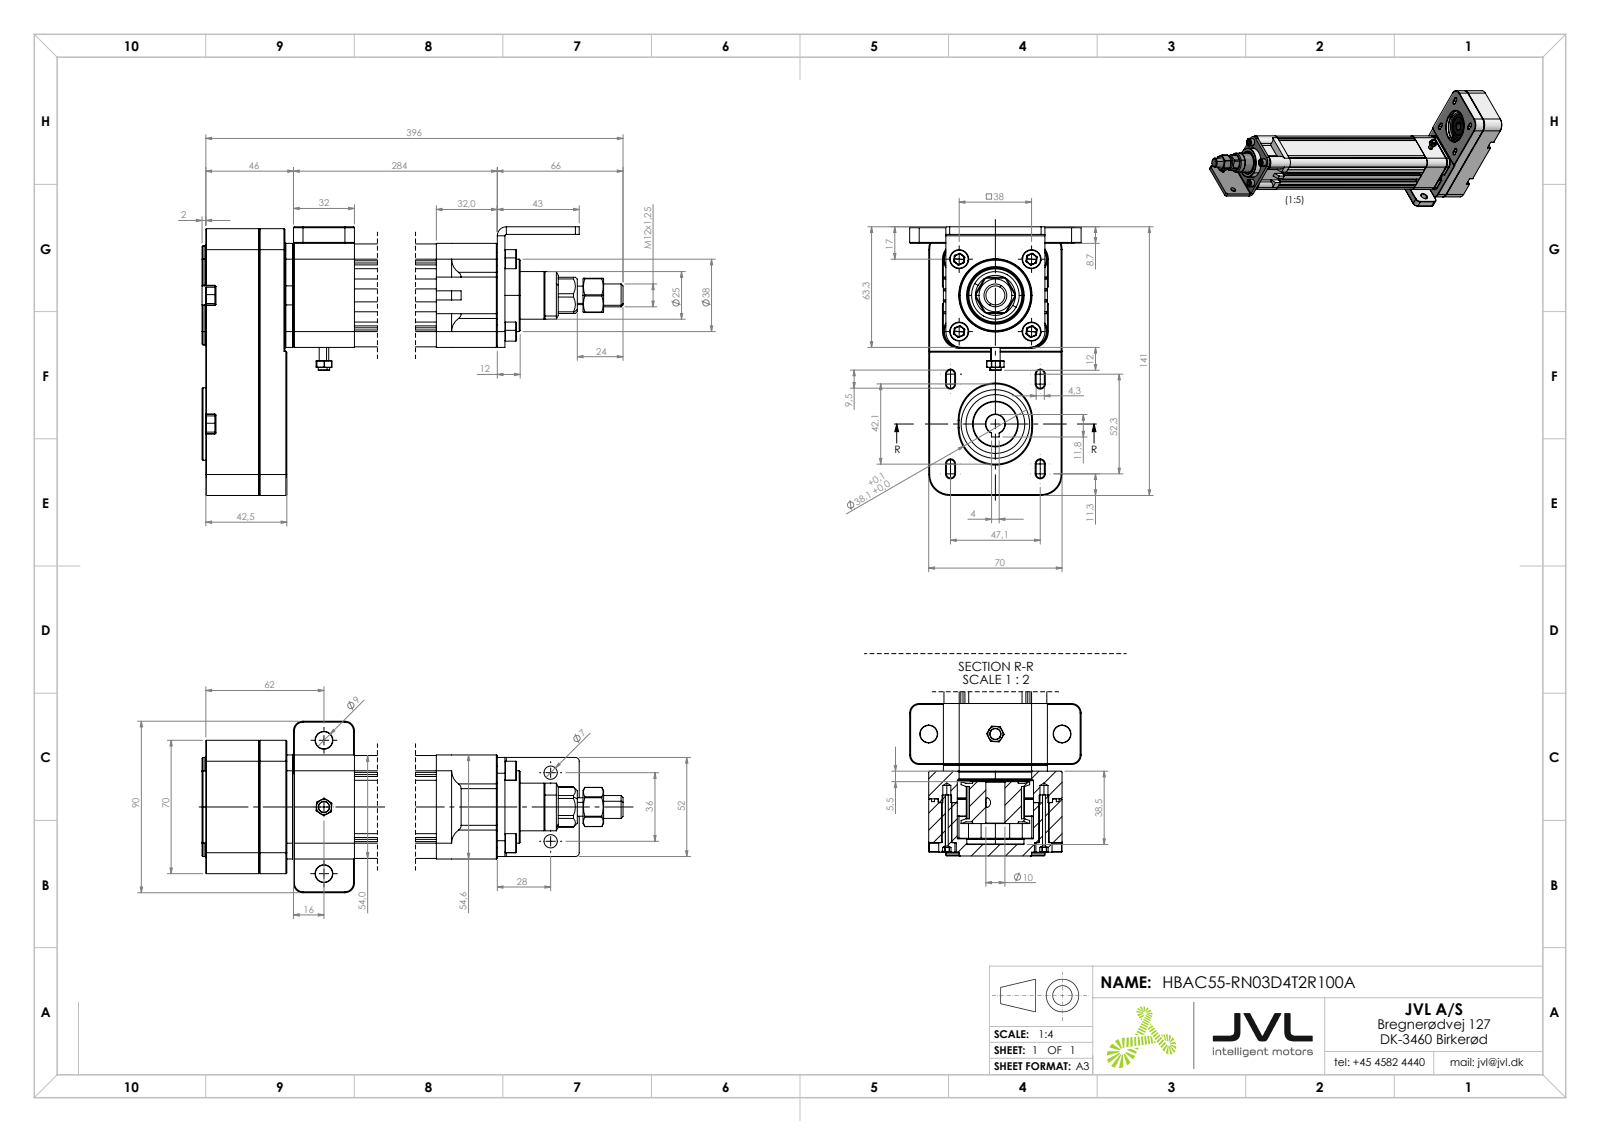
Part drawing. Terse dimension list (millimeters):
name: HBAC55 (CONFIGURABLE); HBAC55-NUT M12x1,25; HBAC55-Back piece T2; HBAC55-M5x25 (+8 more)
written by: SolidWorks 2023 (AUTOMOTIVE_DESIGN)
unit: mm
bodies: 24 solids, 2089 faces (695 planar, 810 cylindrical, 584 other)
size: 398 × 141 × 90
volume: 710 310 mm³; area: 291 163 mm²
holes: 8× ⌀4.2, 6× ⌀5, 5× ⌀1.5, 5× ⌀5.3, 4× ⌀6.4, 4× ⌀6.5, 4× ⌀9.5, 4× ⌀10, 2× ⌀5.5, 2× ⌀7, 2× ⌀9, 2× ⌀11
bosses: 8× ⌀5, 7× ⌀8.5, 6× ⌀10, 5× ⌀6, 2× ⌀38, 1× ⌀36, 1× ⌀25, 1× ⌀24
rounds: 90× R0.25, 84× R0.2, 45× R0.5, 41× R0.55, 41× R3.27, 8× R0.3, 8× R2.15, 8× R3
face distances: 8, 5, 4.5, 54, 62, 3, 31, 4, 9, 54.3
hole spacings: 20.08, 25.5, 26.87, 38, 48.39, 72.16, 67.5, 10
